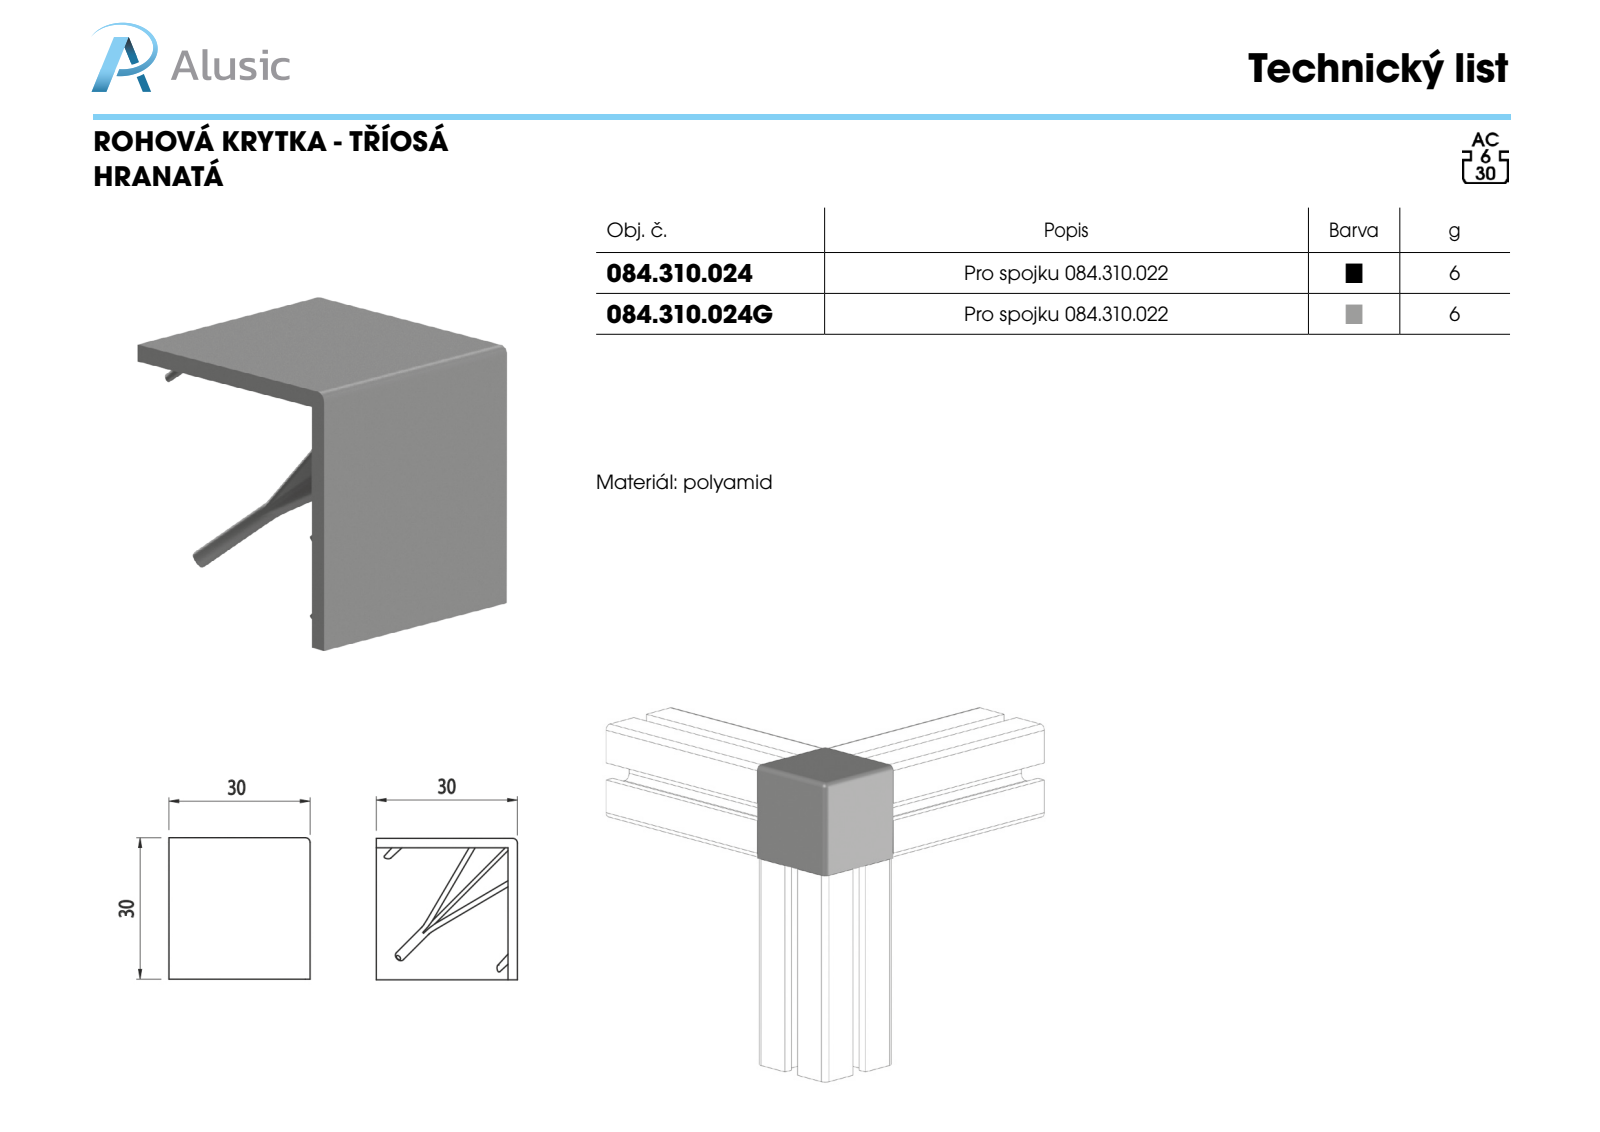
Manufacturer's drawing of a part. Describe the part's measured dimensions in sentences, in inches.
The part is named "084.310.024". Its 3-D file was written by "SolidWorks 2012 (CONFIG_CONTROL_DESIGN)". It is 1 solid with 103 faces: 22 planar, 31 cylindrical and 50 other. Overall it measures 1.181 by 1.181 by 1.181 inches. Its volume is 0.338 cubic inches and its surface area 9.359 square inches. Round bosses or shafts: 1 of diameter 0.083. Partial cylindrical surfaces (rounded edges, fillets, slot ends): 21 of radius 0.02, 3 of radius 0.039. The main face-to-face distances are 0.079, 1.181, 1.102, 0.059, 0.374.
